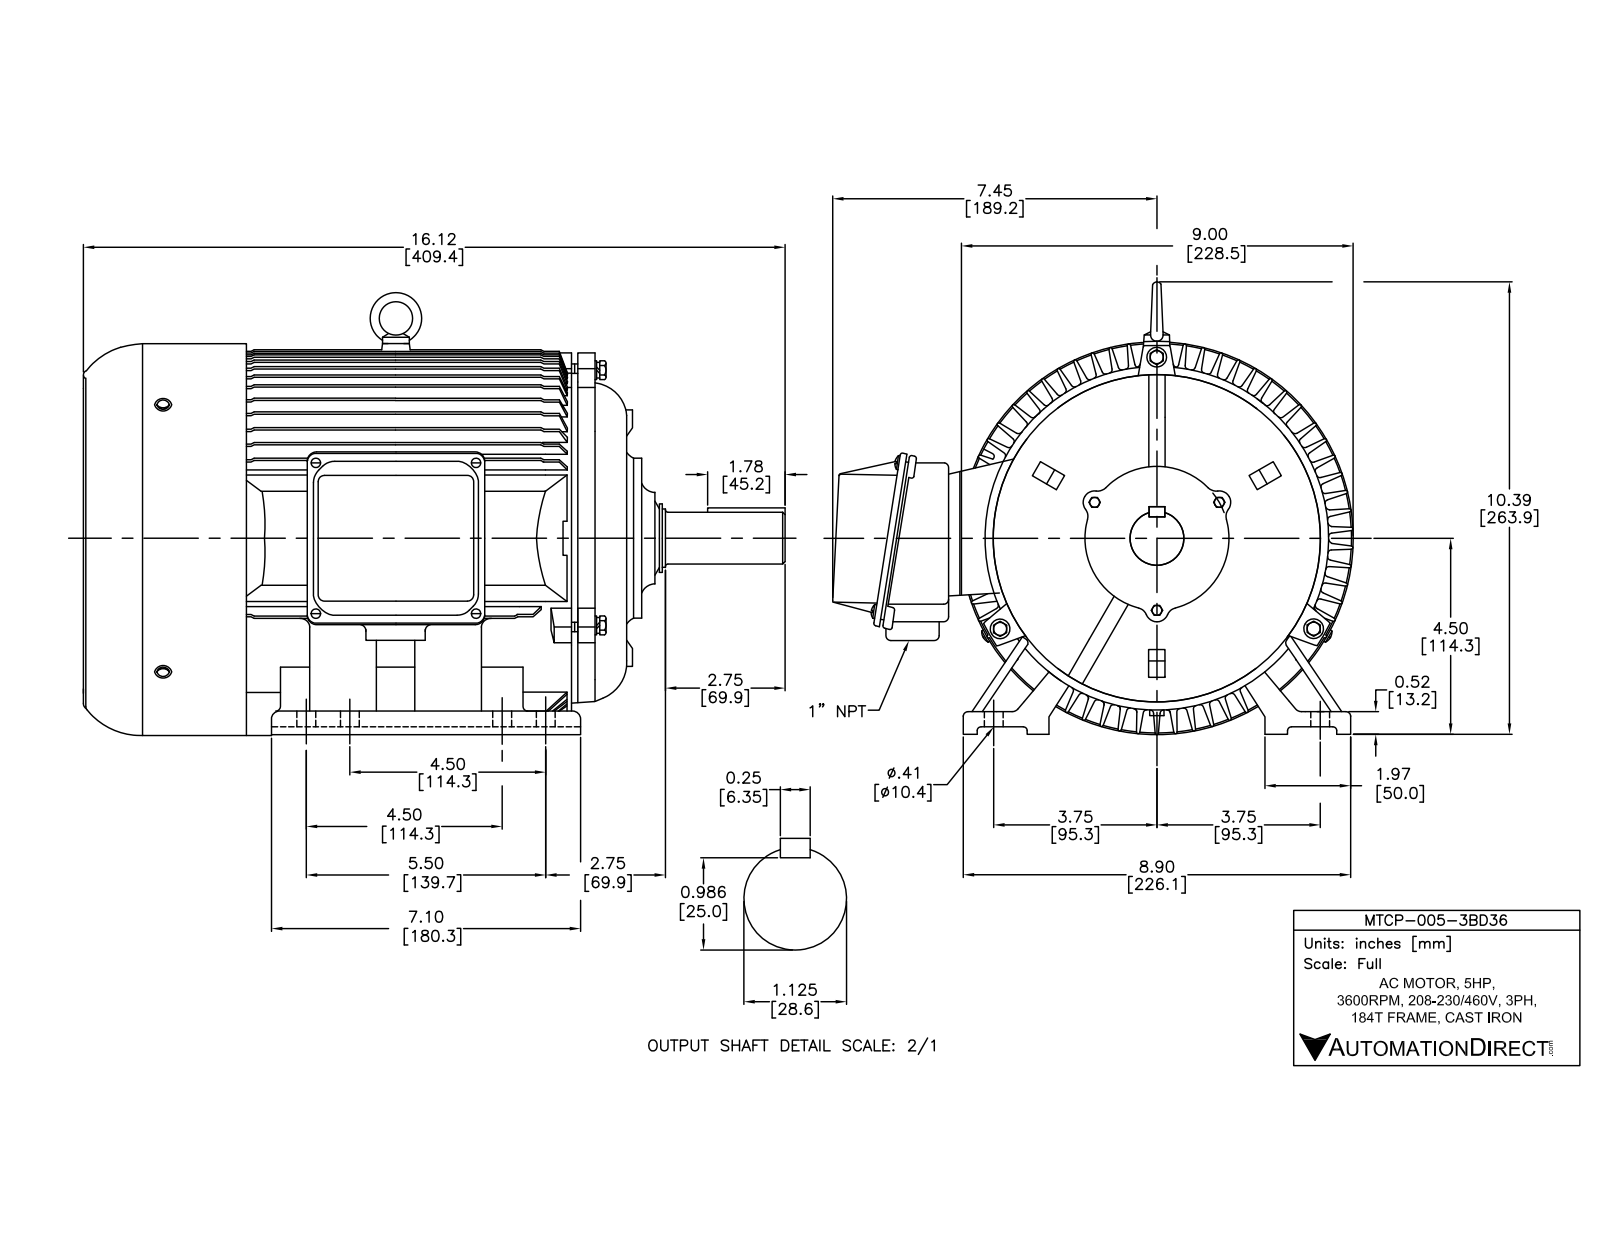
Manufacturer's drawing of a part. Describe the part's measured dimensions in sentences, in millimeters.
The part is named "spring lock washers--normal type gb_GB_FASTENER_WASHER_SW 5; eyebolts gb_GB_FASTENER_SCREWS_FRS M8-N; PE180接线盒座_默认_按加工; plain washers-chamfered--normal series-a gb_GB_FASTENER_WASHER_SWCA 8 (+6 more)". Its 3-D file was written by "SolidWorks 2017 (AUTOMOTIVE_DESIGN)". It is 48 solids with 2786 faces: 734 planar, 1008 cylindrical and 1044 other. Overall it measures 410.6 by 300.92 by 265.4 millimeters. Its volume is 2 705 000 cubic millimeters and its surface area 1 021 000 square millimeters. Round holes: 15 of diameter 5.8, 11 of diameter 4.2, 8 of diameter 10.5, 4 of diameter 6.8, 3 of diameter 5.3, 3 of diameter 5.4, 3 of diameter 8.4, 3 of diameter 8.68, 3 of diameter 10, 2 of diameter 8, 1 of diameter 13, 1 of diameter 30. Round bosses or shafts: 11 of diameter 5, 7 of diameter 8, 3 of diameter 16, 3 of diameter 12.88, 3 of diameter 10, 1 of diameter 219.4, 1 of diameter 194, 1 of diameter 193. Partial cylindrical surfaces (rounded edges, fillets, slot ends): 222 of radius 1, 67 of radius 0.5, 59 of radius 2, 47 of radius 3, 33 of radius 1.25, 22 of radius 7, 16 of radius 0.34, 11 of radius 8. The main face-to-face distances are 3, 5, 6, 1.2, 266, 243, 237, 4, 23, 10. The hole center spacings are 68, 100, 25.4, 68.01, 96.17, 114.3, 190.5, 192.19.
